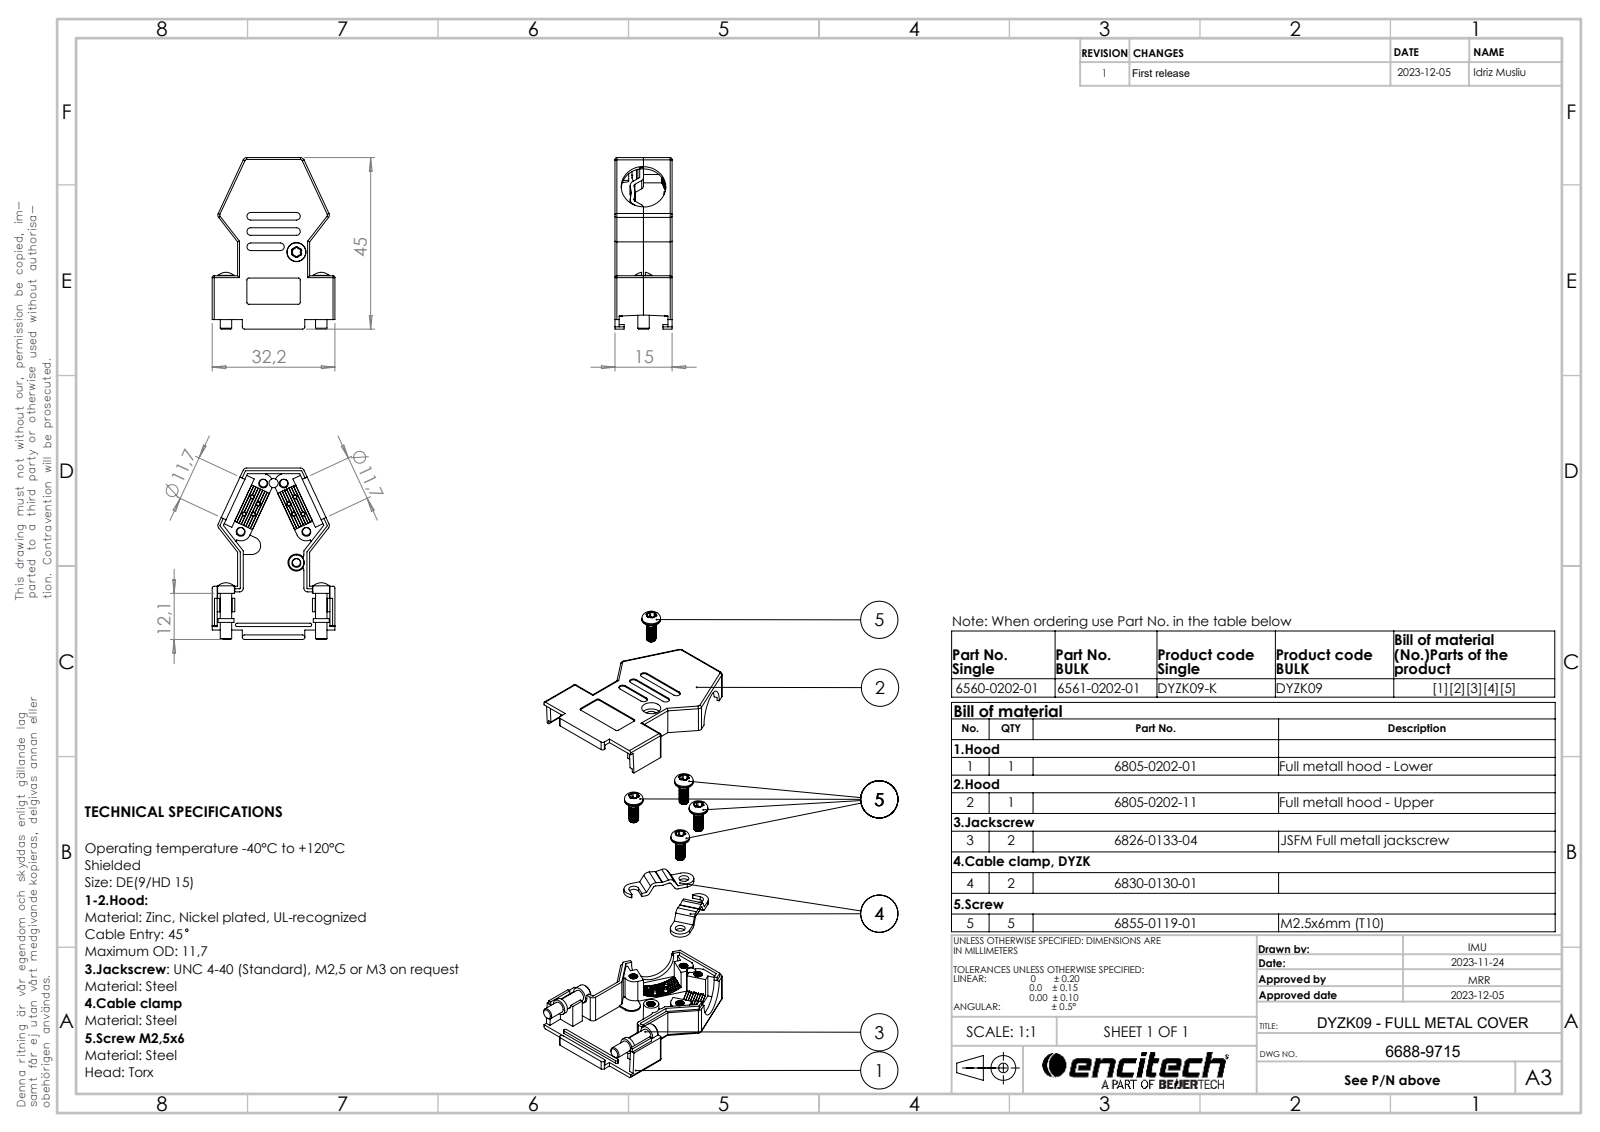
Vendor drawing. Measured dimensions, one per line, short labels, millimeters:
name: 6805-0202-01; 6688-9715; 6805-0202-11; 6826-0133-04 (+2 more)
written by: SolidWorks 2021 (AUTOMOTIVE_DESIGN)
unit: mm
bodies: 11 solids, 1082 faces (345 planar, 581 cylindrical, 156 other)
size: 45 × 32.2 × 15
volume: 5 804 mm³; area: 10 238 mm²
holes: 4× ⌀2.03, 2× ⌀2.6, 2× ⌀3.2, 2× ⌀4.6, 1× ⌀2.05, 1× ⌀2.8, 1× ⌀5
bosses: 5× ⌀4.9, 5× ⌀2.5, 2× ⌀4.4, 2× ⌀4.2, 2× ⌀3, 1× ⌀4.3, 1× ⌀2.4
rounds: 32× R0.5, 30× R0.18, 30× R0.7, 17× R1, 8× R2.6, 6× R1.5, 4× R5.85, 2× R0.1
face distances: 1.1, 13.9, 15, 12.8, 0.8, 7.5, 6.4, 1.5, 1.4, 1
hole spacings: 13.99, 17, 5.4, 8.57, 16.74, 17.24, 21.1, 22.58
